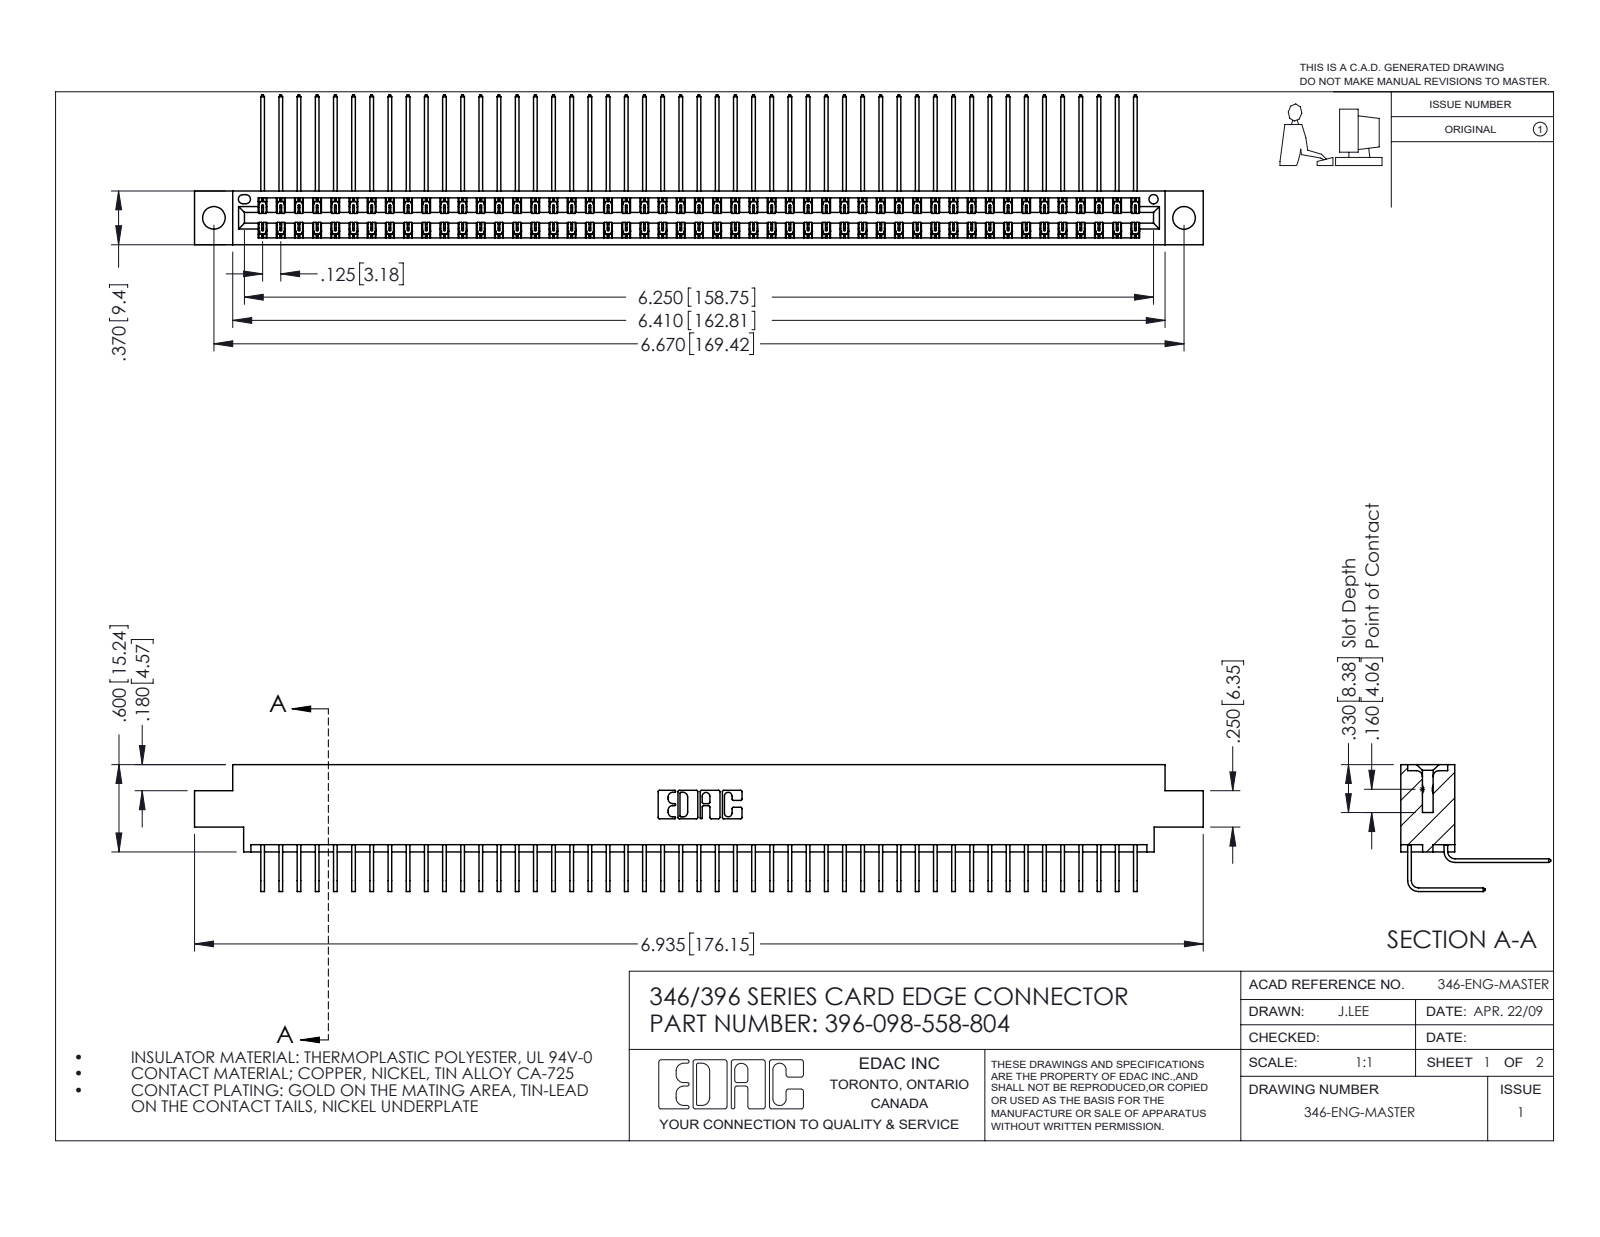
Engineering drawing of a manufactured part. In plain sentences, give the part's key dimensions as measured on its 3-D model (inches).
The part is named "396-098-558-804; 345-292-001_558 559 Tail - 1; 346 Part_0.170 Offset - 0.156 Dia-TH; 345-292-001_558 Tail - 2". Its 3-D file was written by "SolidWorks 2016 (CONFIG_CONTROL_DESIGN)". It is 99 solids with 5418 faces: 3706 planar, 1712 cylindrical and 0 other. Overall it measures 6.935 by 1.03 by 0.873 inches. Its volume is 1.071 cubic inches and its surface area 41.76 square inches. Round holes: 2 of diameter 0.156, 1 of diameter 0.064. Partial cylindrical surfaces (rounded edges, fillets, slot ends): 147 of radius 0.006, 22 of radius 0.01, 6 of radius 0.007, 6 of radius 0.031, 3 of radius 0.026, 2 of radius 0.014, 2 of radius 0.022, 2 of radius 0.024. The main face-to-face distances are 0.322, 0.048, 0.025, 0.37, 0.25, 0.298, 0.072, 0.275, 0.148, 0.222. The hole center spacings are 0.246, 6.461, 6.67.
